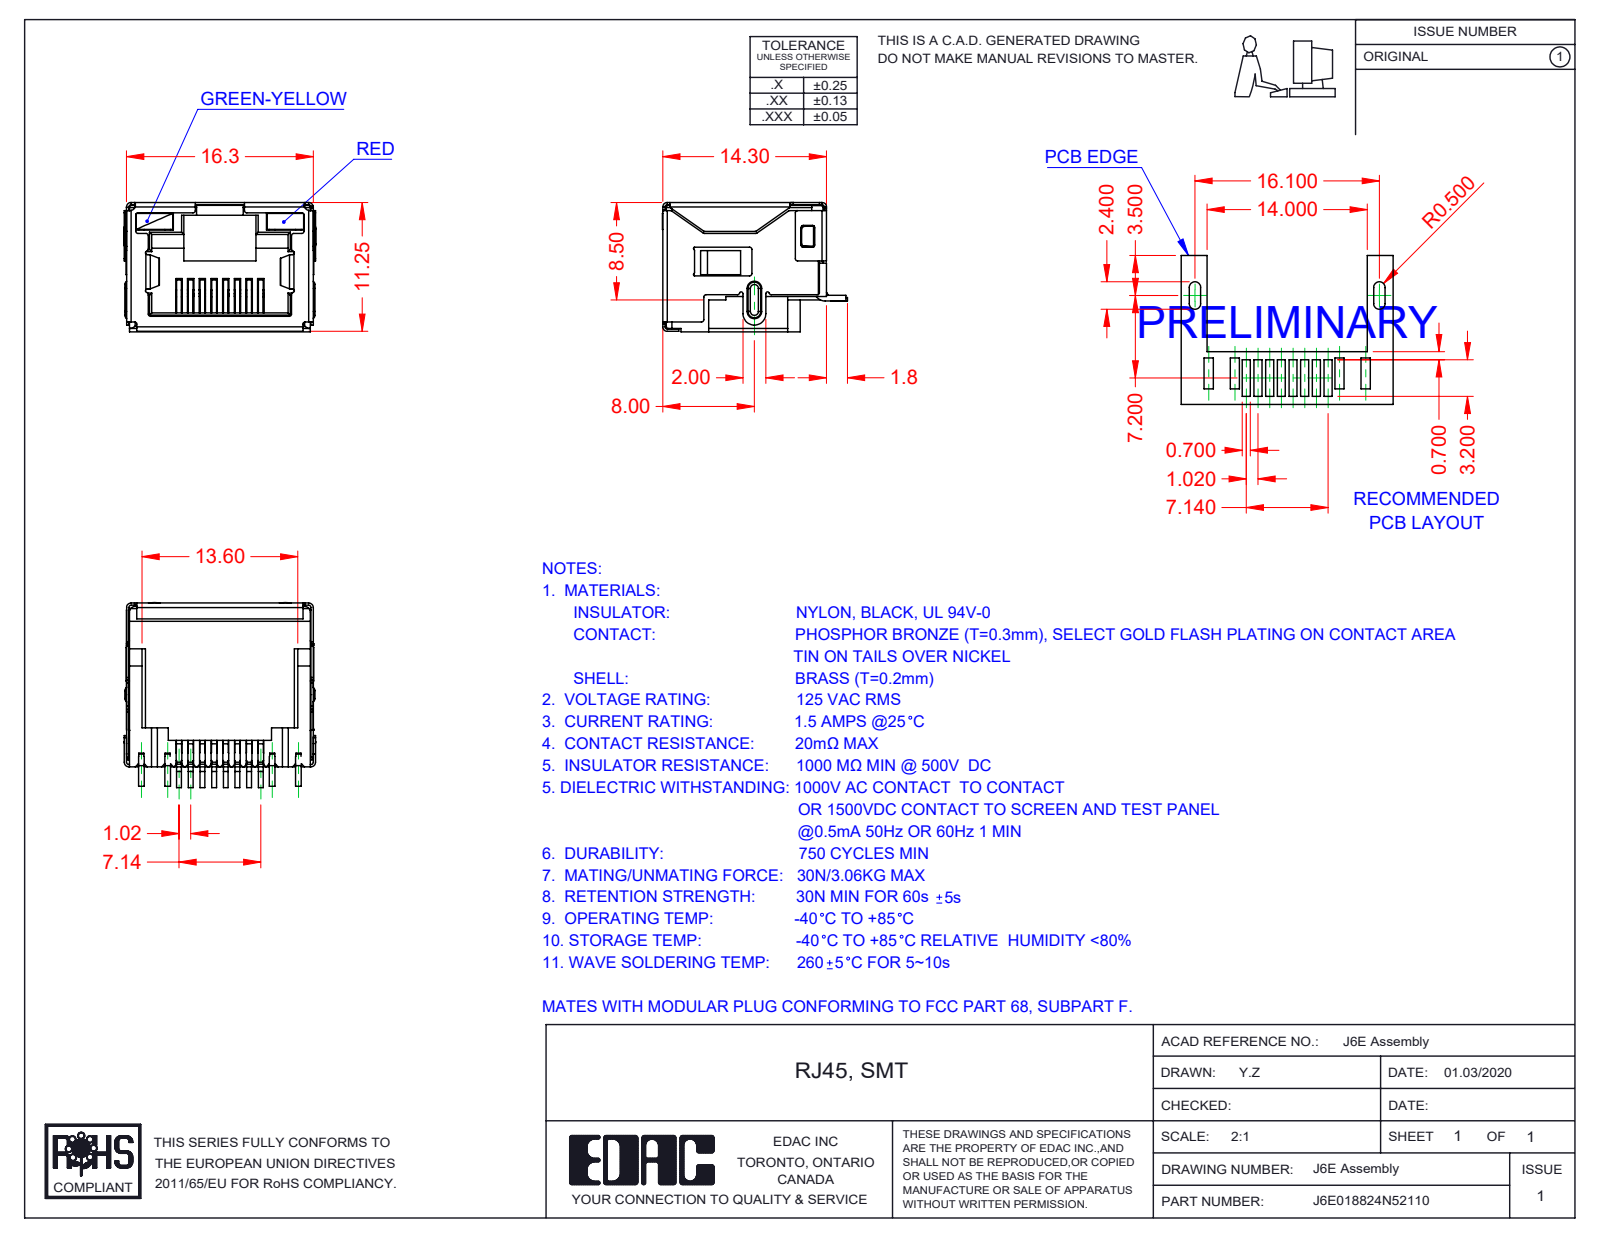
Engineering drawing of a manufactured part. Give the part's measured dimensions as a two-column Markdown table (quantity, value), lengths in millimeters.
| quantity | value |
| --- | --- |
| part name | 6E LED LH_5-Green-Yellow; 6E Shield_LED; 6E Contacts; 6E Insulator_LED (+2 more) |
| STEP written by | SolidWorks 2016 (CONFIG_CONTROL_DESIGN) |
| units | millimeters |
| bodies | 12 solids, 1498 faces (1099 planar, 349 cylindrical, 50 other) |
| overall size | 16.75 × 16.15 × 11.3 |
| volume | 1 109 mm³ |
| surface area | 4 045 mm² |
| partial cylindrical surfaces (radius × count) | 0.2 × 82, 0.25 × 17, 0.4 × 13, 0.5 × 13, 0.1 × 10, 0.15 × 7, 0.3 × 4, 1 × 3 |
| main face-to-face distances | 11.05, 16.05, 16.1, 15.85, 11.1, 11.3, 2.4, 0.7, 9.85, 0.49 |
